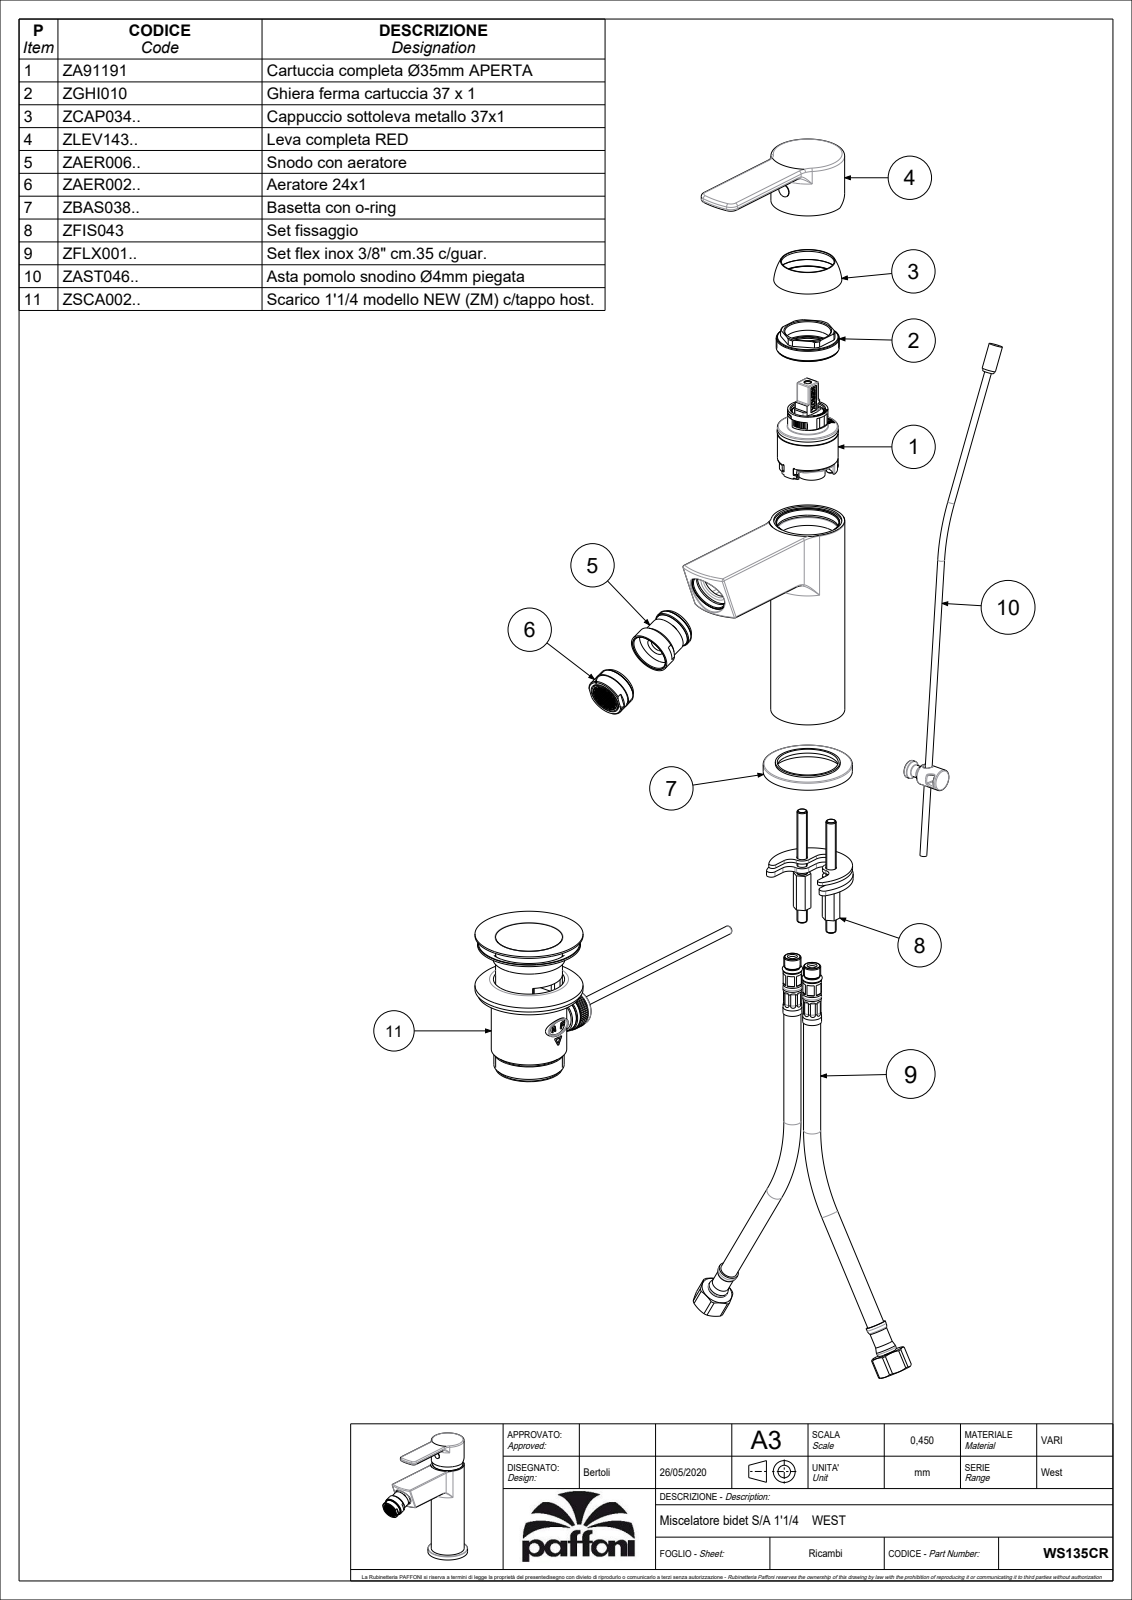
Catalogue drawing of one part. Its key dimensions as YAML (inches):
part_name: "WS135CR"
step_written_by: "CREO PARAMETRIC BY PTC INC, 2020044 (CONFIG_CONTROL_DESIGN)"
units: inches
bodies: {solids: 5, faces: 3498, planar: 2450, cylindrical: 573, other: 475}
overall_size: [6.419, 6.4, 2.047]
volume: 10.84
surface_area: 167.4
round_holes:
  - {diameter: 0.181, count: 3}
  - {diameter: 0.217, count: 3}
  - {diameter: 0.315, count: 3}
  - {diameter: 0.276, count: 2}
  - {diameter: 0.354, count: 2}
  - {diameter: 0.433, count: 2}
  - {diameter: 0.118, count: 1}
  - {diameter: 0.134, count: 1}
  - {diameter: 0.138, count: 1}
  - {diameter: 0.157, count: 1}
  - {diameter: 0.177, count: 1}
  - {diameter: 0.61, count: 1}
round_bosses_or_shafts:
  - {diameter: 0.425, count: 2}
  - {diameter: 0.323, count: 2}
  - {diameter: 0.236, count: 2}
  - {diameter: 0.189, count: 2}
  - {diameter: 0.157, count: 2}
  - {diameter: 2.047, count: 1}
  - {diameter: 1.701, count: 1}
  - {diameter: 1.693, count: 1}
partial_cylinders:
  - {radius: 0.02, count: 85}
  - {radius: 0.059, count: 33}
  - {radius: 0.039, count: 19}
  - {radius: 0.079, count: 9}
  - {radius: 0.067, count: 6}
  - {radius: 0.031, count: 4}
  - {radius: 0.197, count: 4}
  - {radius: 0.228, count: 4}
face_to_face_distances: [0.138, 1.083, 0.177, 1.4, 1.004, 1.222, 1.22, 1.142, 2.364, 2.541]
hole_center_spacings: [0.02, 0.339, 0.355, 0.53, 0.571, 0.593, 0.596, 0.863]
